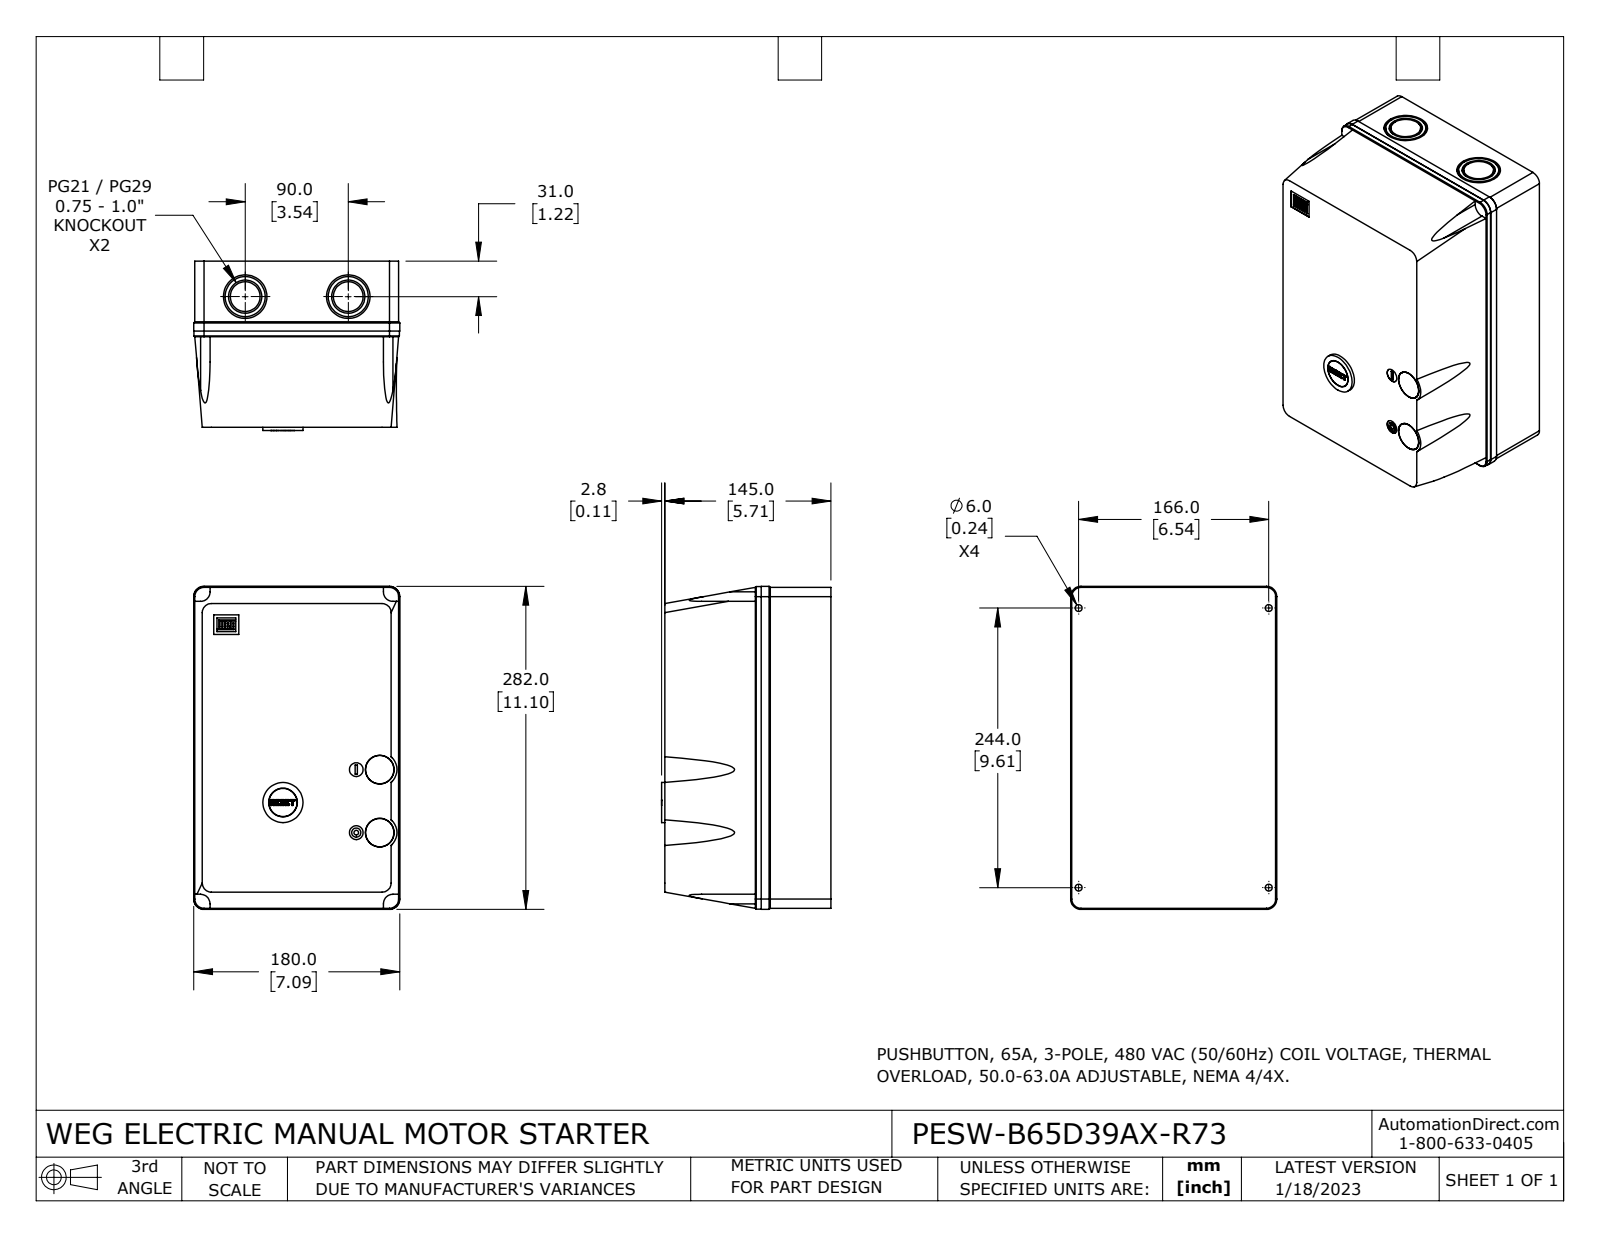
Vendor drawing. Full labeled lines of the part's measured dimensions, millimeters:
Part name (STEP PRODUCT): PESW-B65D39AX-R73
STEP written by: SolidWorks 2021 (CONFIG_CONTROL_DESIGN)
Units: millimetres
Bodies: 3 solids, 286 faces (130 planar, 144 cylindrical, 12 other)
Overall size (bounding box): 282 × 180 × 147.9
Volume: 7 014 000 mm³ · Surface area: 232 257 mm²
Round holes (diameter × count): ⌀6 ×4, ⌀25 ×3, ⌀12 ×2, ⌀29 ×2, ⌀38 ×2, ⌀4 ×1, ⌀30.5 ×1
Round bosses / shafts (diameter × count): ⌀35 ×3, ⌀26 ×2, ⌀24.8 ×2, ⌀30.3 ×1, ⌀24.6 ×1, ⌀14 ×1, ⌀8 ×1
Partial cylindrical surfaces — rounded edges, fillets, slot ends (radius × count): R0.1 ×34, R8 ×4, R8.3 ×4, R8.7 ×4, R9 ×4, R1.6 ×1
Main face-to-face distances: 145, 178, 280, 1, 0.7, 179, 179.7, 178.7, 281, 180
Hole centre spacings: 20.5, 55, 58.7, 166, 244, 295.11, 49.14, 57.14
